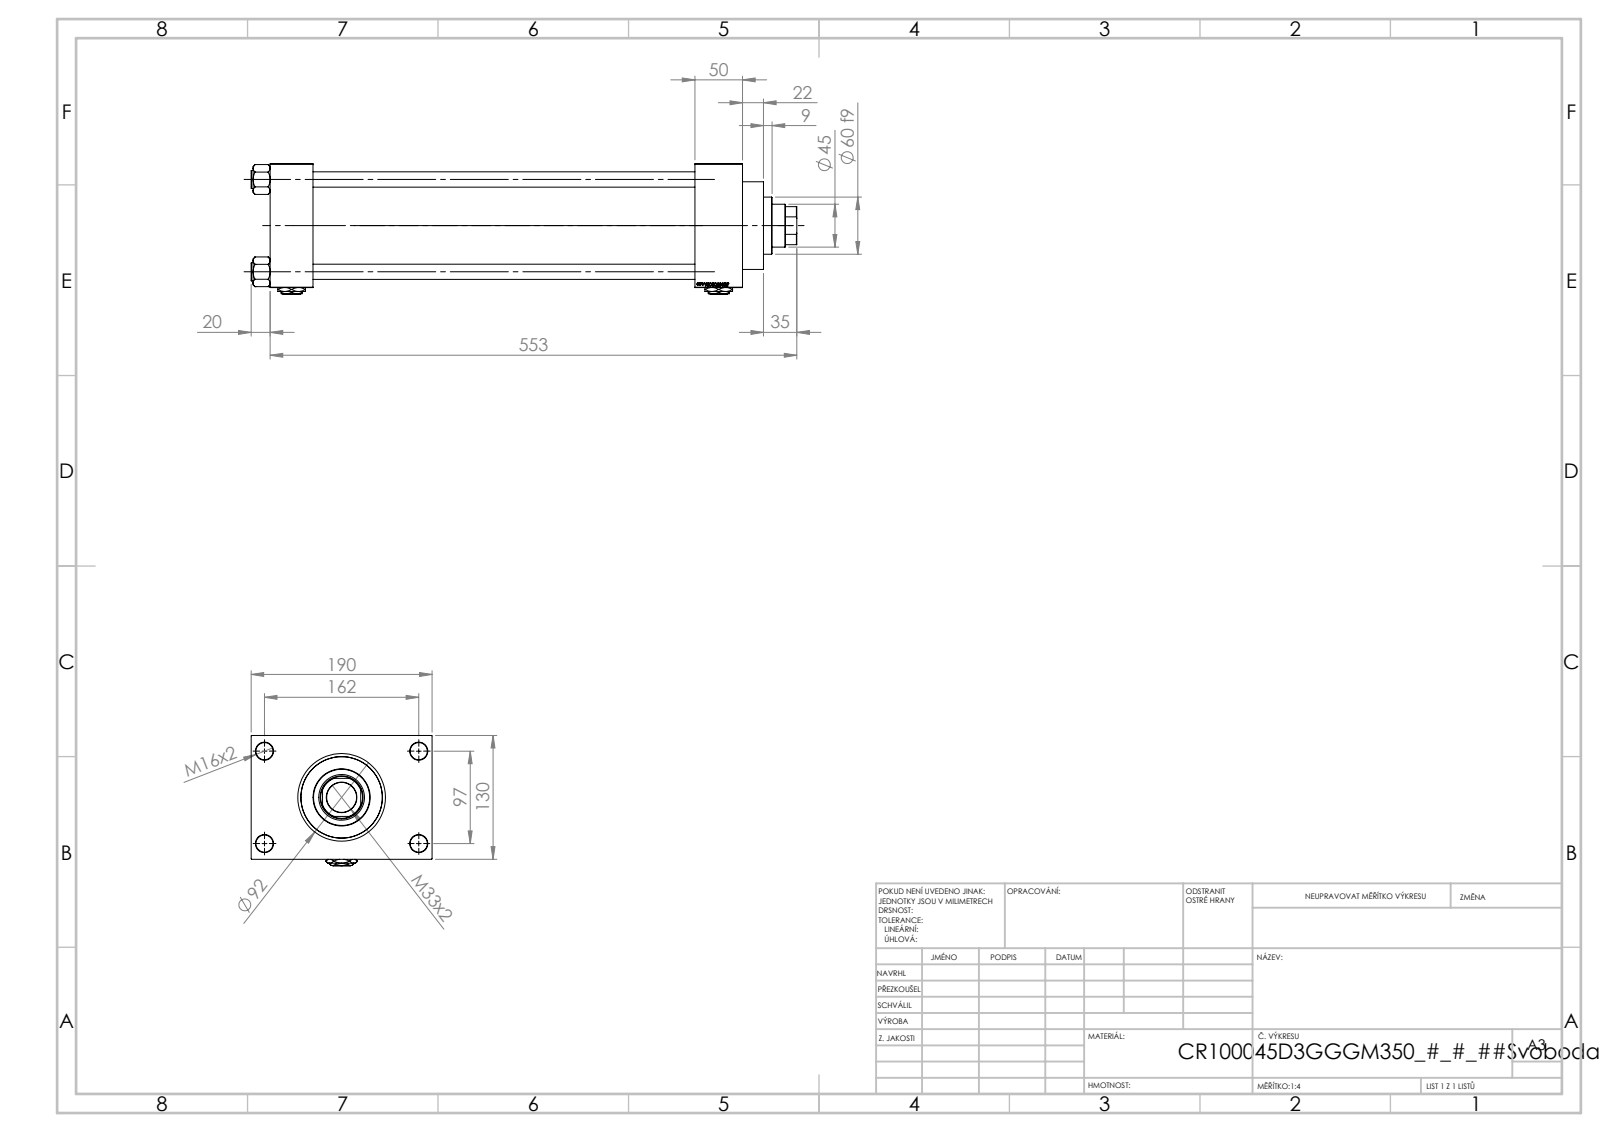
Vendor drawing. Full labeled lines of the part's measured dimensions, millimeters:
Part name (STEP PRODUCT): NUT_M5_D; Zatka_pro_OIL_PORT; V215CR_D_TYCINKA; V215CR_D_Body (+2 more)
STEP written by: SolidWorks 2019 (CONFIG_CONTROL_DESIGN)
Units: millimetres
Bodies: 13 solids, 1253 faces (593 planar, 100 cylindrical, 560 other)
Overall size (bounding box): 573 × 190 × 137
Volume: 3 703 000 mm³ · Surface area: 685 881 mm²
Round holes (diameter × count): ⌀16 ×4, ⌀18 ×4, ⌀7 ×2, ⌀26.44 ×2, ⌀35 ×2, ⌀31.5 ×1, ⌀45 ×1, ⌀48 ×1, ⌀76 ×1, ⌀85.5 ×1, ⌀100 ×1
Round bosses / shafts (diameter × count): ⌀19 ×4, ⌀106 ×1, ⌀92 ×1, ⌀60 ×1
Partial cylindrical surfaces — rounded edges, fillets, slot ends (radius × count): R22 ×1
Main face-to-face distances: 130, 45, 446, 401, 496, 451, 50, 30, 160, 190
Hole centre spacings: 32.55, 68.52, 94.41, 96.9, 102.27, 129.45, 161.73, 97
